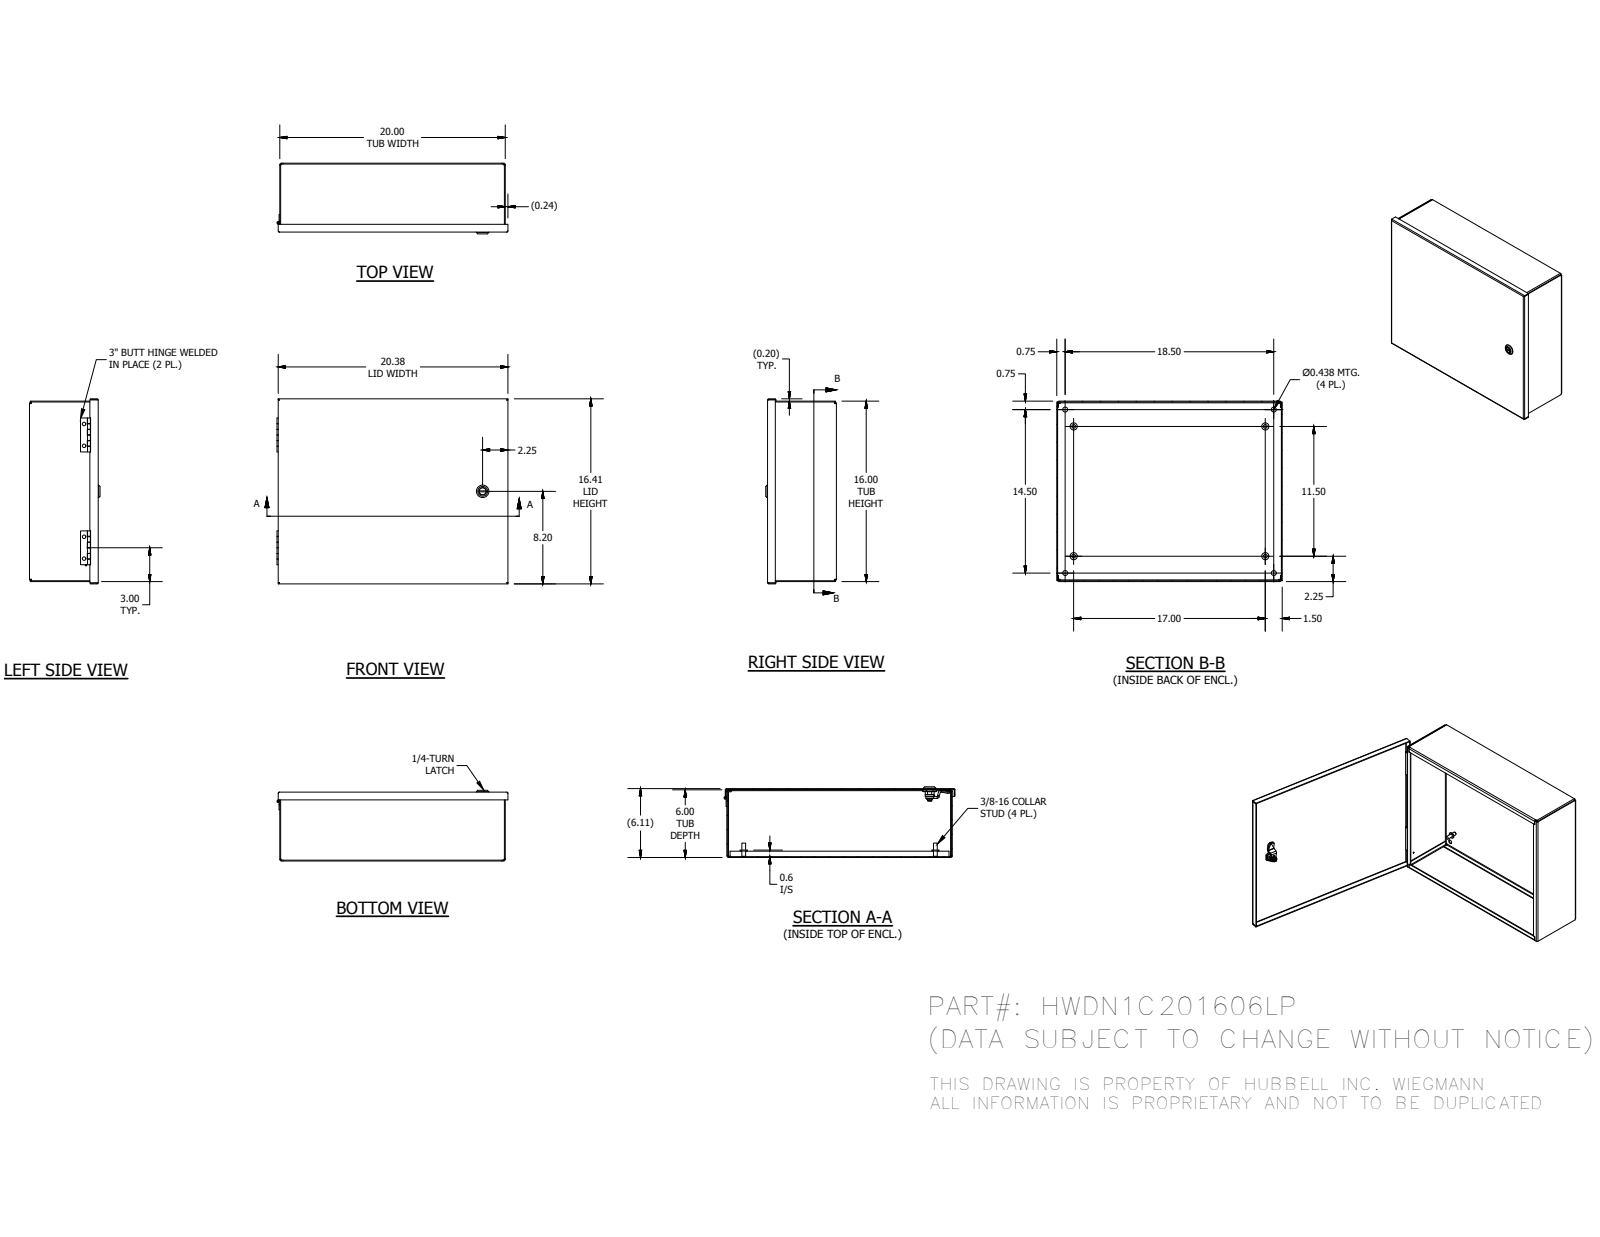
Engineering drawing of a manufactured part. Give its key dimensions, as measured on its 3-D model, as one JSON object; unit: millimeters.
{"part_name": "N1C201606LPBLR; N1C2006LPTB; N1C2016LPLID; 1000-101-GPF_GPD (+8 more)", "step_written_by": "Autodesk Inventor 2016 (AUTOMOTIVE_DESIGN)", "units": "millimeters", "bodies": {"solids": 21, "faces": 717, "planar": 437, "cylindrical": 212, "other": 68}, "overall_size": [520.41, 416.72, 178.12], "volume_mm3": 1522000, "surface_area_mm2": 1632000, "round_holes": [[7.95, 4], [11.11, 4], [3.05, 1], [3.3, 1], [5, 1], [8, 1], [10, 1], [10.2, 1], [16.1, 1], [20.38, 1]], "round_bosses_or_shafts": [[15.88, 4], [8.38, 4], [28, 1], [27, 1], [23, 1], [19.8, 1], [15.8, 1], [15.2, 1]], "partial_cylinders_radius": [[0.3, 30], [1.59, 12], [3.47, 12], [0.5, 10], [0.79, 4], [2.67, 4], [4, 4], [0.4, 3]], "face_to_face_distances": [1.88, 172.24, 170.36, 174.12, 404.52, 506.12, 402.64, 406.4, 504.24, 508], "hole_center_spacings": [49.28, 186.92, 254, 368.3, 469.9, 475.01, 597.04, 15.51]}
